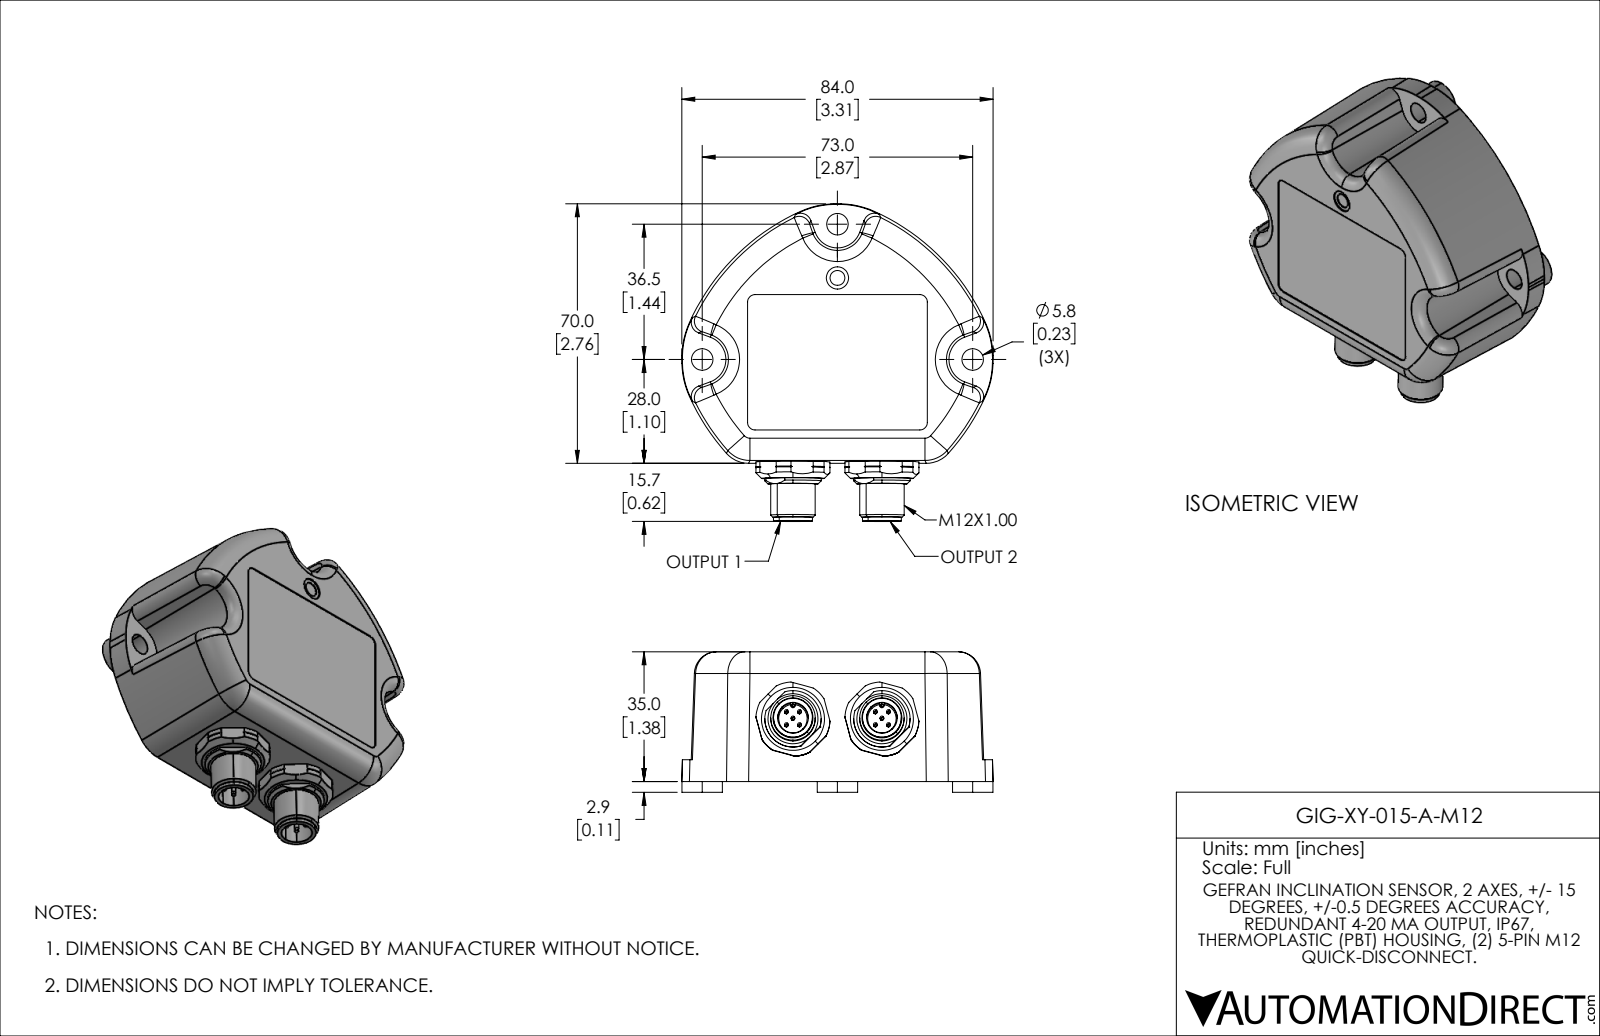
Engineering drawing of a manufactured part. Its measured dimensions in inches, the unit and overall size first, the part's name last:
Units: inches
Overall size (bounding box): 3.374 × 3.307 × 1.492
Round holes (diameter × count): ⌀0.228 ×3, ⌀0.327 ×2, ⌀0.157 ×1, ⌀0.236 ×1
Round bosses / shafts (diameter × count): ⌀0.039 ×10, ⌀0.429 ×3, ⌀0.472 ×2, ⌀0.413 ×2
Partial cylindrical surfaces — rounded edges, fillets, slot ends (radius × count): R0.02 ×4, R0.079 ×4, R0.299 ×3, R0.024 ×2, R0.273 ×2, R0.394 ×2, R0.236 ×1, R0.301 ×1
Main face-to-face distances: 1.37, 1.378, 0.232, 1.138, 1.146, 0.114, 0.346, 1.484, 1.492, 0.668
Hole centre spacings: 1.678, 2.032, 0.571, 0.945, 2.874
Volume: 9.029 in³ · Surface area: 32.38 in²
Bodies: 1 solid, 365 faces (87 planar, 123 cylindrical, 155 other)
Part name (STEP PRODUCT): GIG-XY-015-A-M12
STEP written by: SolidWorks 2021 (AUTOMOTIVE_DESIGN)
